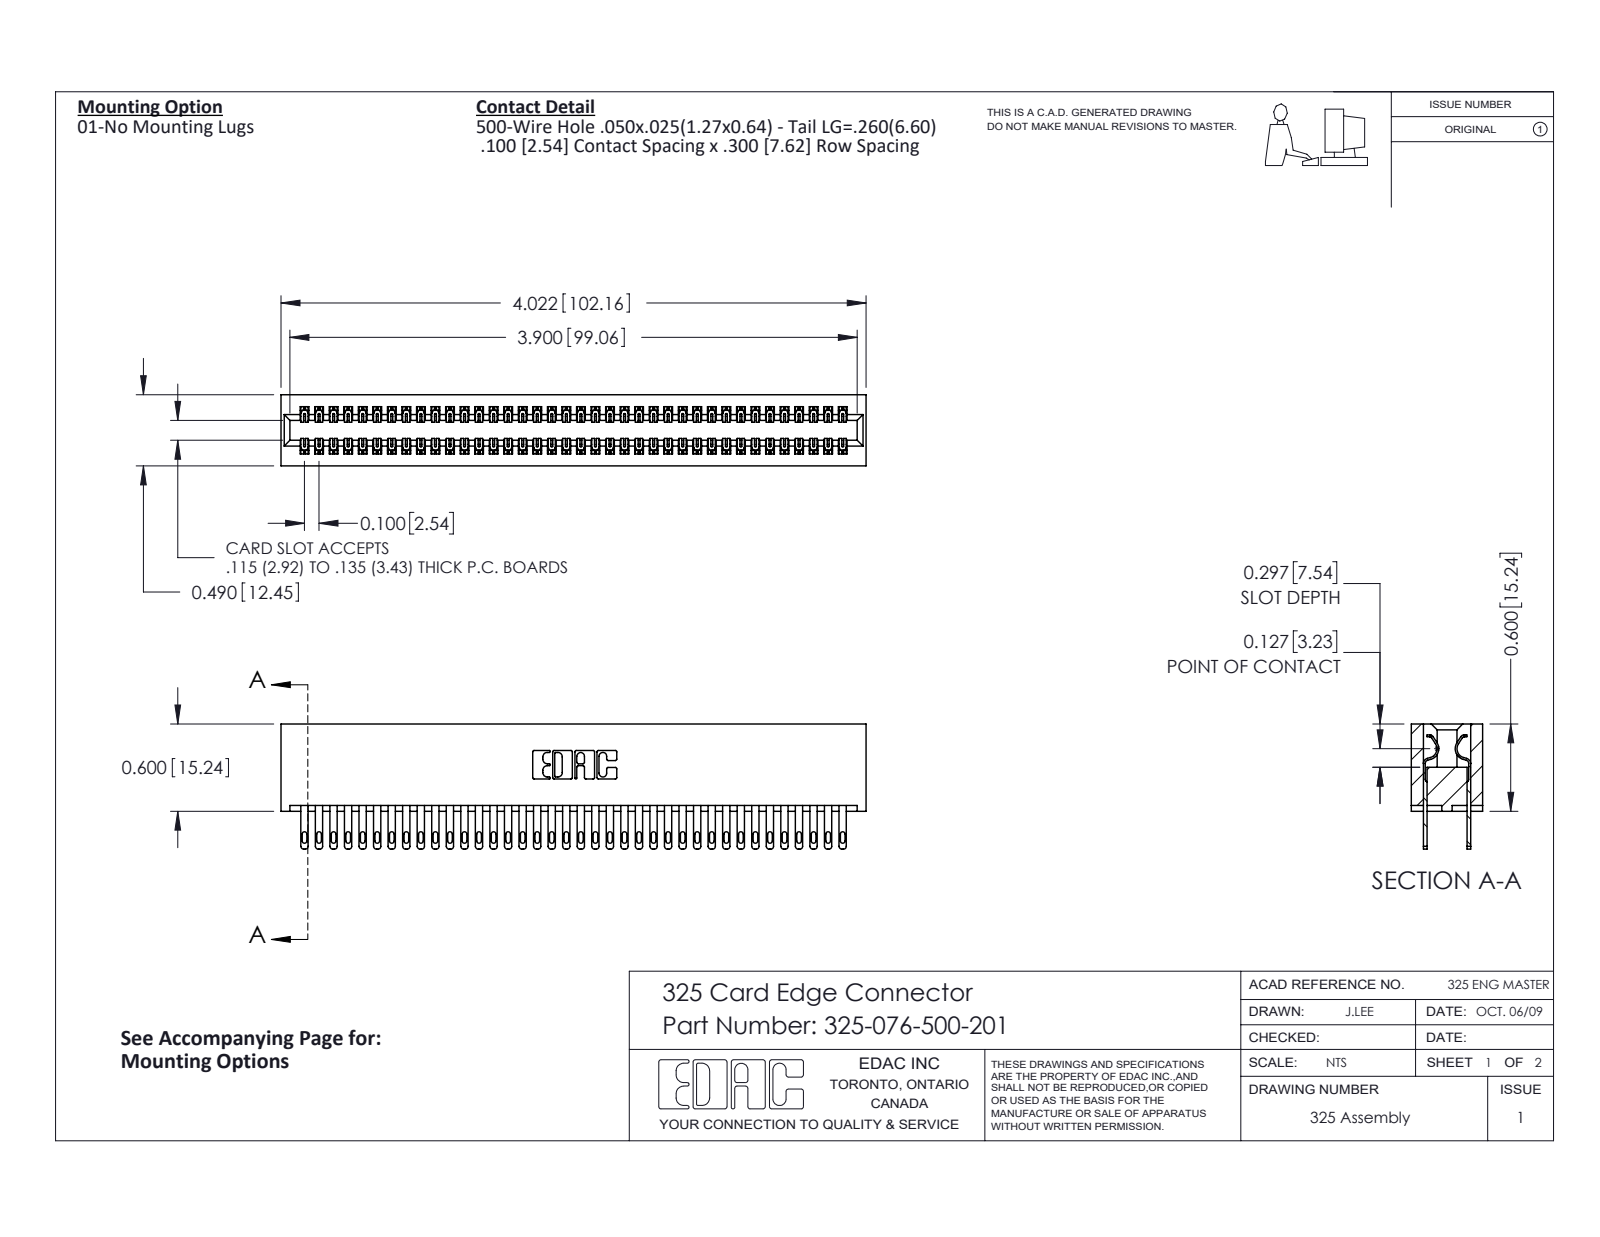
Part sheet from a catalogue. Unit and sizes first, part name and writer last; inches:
Units: inches
Overall size (bounding box): 4.022 × 0.86 × 0.49
Partial cylindrical surfaces — rounded edges, fillets, slot ends (radius × count): R0.006 ×114, R0.016 ×76, R0.02 ×76, R0.01 ×22, R0.007 ×6, R0.031 ×6, R0.026 ×3, R0.014 ×2
Main face-to-face distances: 0.083, 0.407, 0.3, 0.107, 0.383, 0.025, 0.325, 0.49, 0.275, 0.56
Volume: 0.854 in³ · Surface area: 28.36 in²
Bodies: 77 solids, 3754 faces (2346 planar, 1408 cylindrical, 0 other)
Part name (STEP PRODUCT): 325 Part_Lugless; 325-076-500-201; 325-292-001_325-293-100
STEP written by: SolidWorks 2016 (CONFIG_CONTROL_DESIGN)
